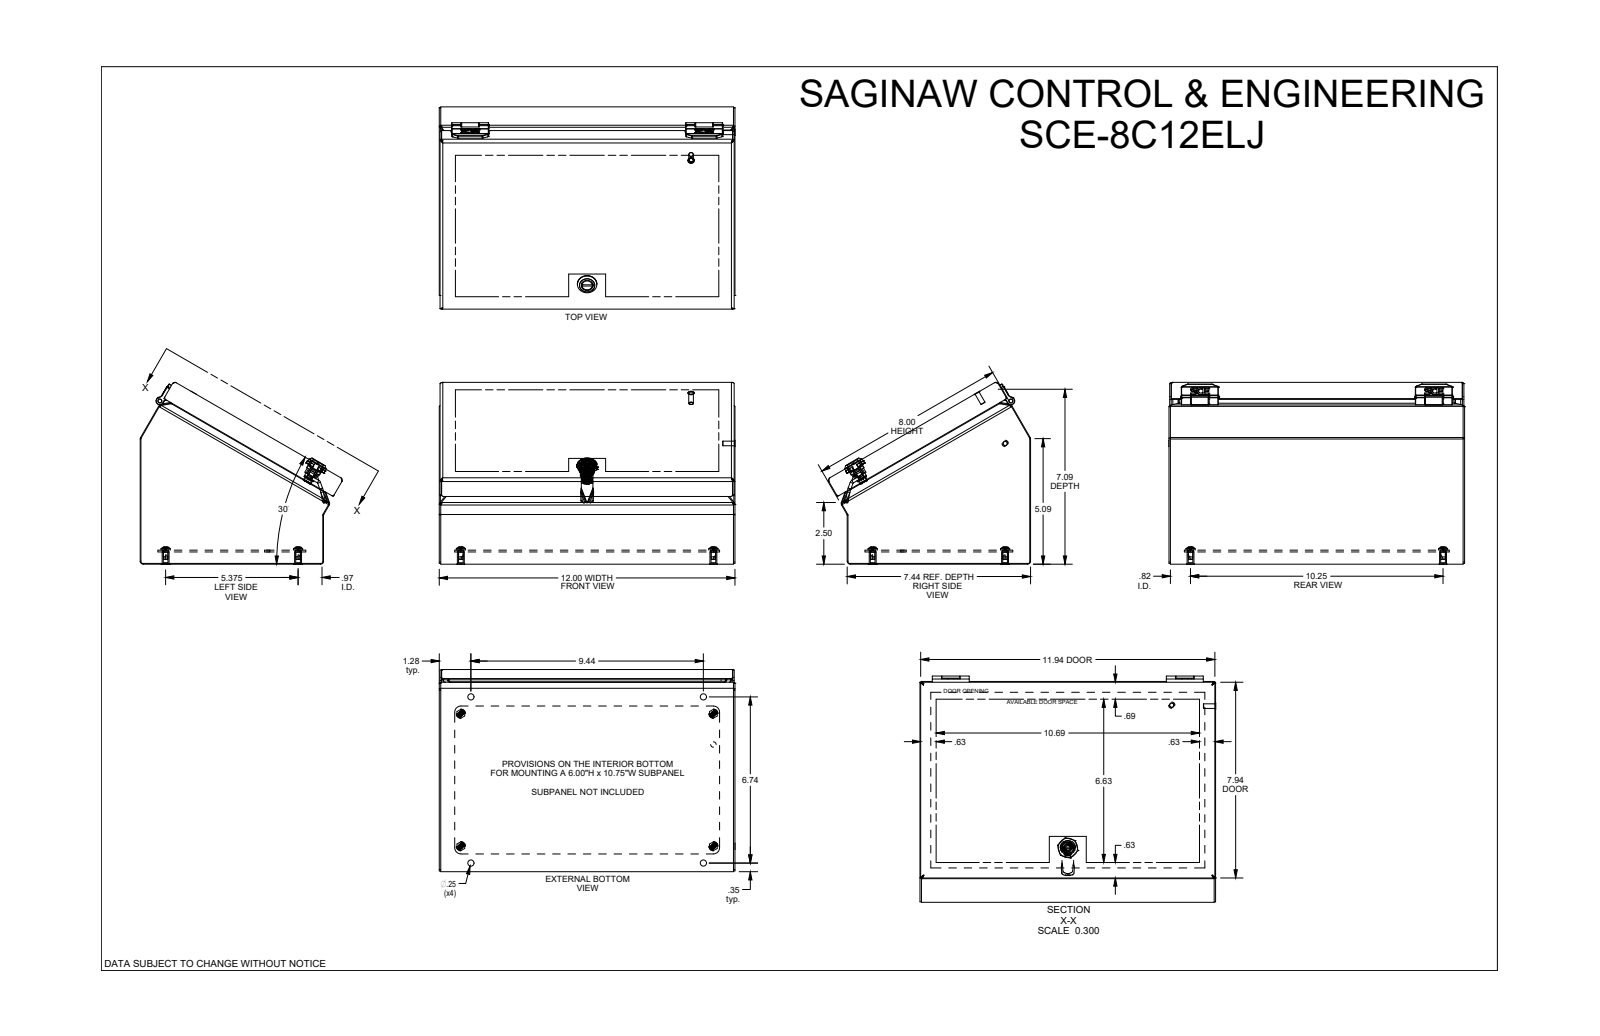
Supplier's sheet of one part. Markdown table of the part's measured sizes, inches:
| quantity | value |
| --- | --- |
| part name | SCE-8C12ELJ |
| STEP written by | SolidWorks 2019 (AUTOMOTIVE_DESIGN) |
| units | inches |
| bodies | 24 solids, 1046 faces (426 planar, 434 cylindrical, 186 other) |
| overall size | 12.004 × 8.201 × 7.38 |
| volume | 33.8 in³ |
| surface area | 1 059 in² |
| round holes (diameter × count) | 0.25 × 8, 0.19 × 4, 0.281 × 4, 0.02 × 2, 0.1 × 2, 0.174 × 2, 0.193 × 2, 0.266 × 2, 0.158 × 1, 0.188 × 1, 0.2 × 1, 0.218 × 1 |
| round bosses / shafts (diameter × count) | 0.28 × 4, 0.26 × 2, 0.256 × 2, 0.188 × 2, 0.18 × 2, 0.788 × 1, 0.548 × 1, 0.46 × 1 |
| partial cylindrical surfaces (radius × count) | 0.008 × 32, 0.03 × 24, 0.06 × 22, 0.013 × 21, 0.015 × 20, 0.12 × 16, 0.01 × 14, 0.02 × 9 |
| main face-to-face distances | 0.06, 0.06, 11.94, 0.436, 0.496, 0.075, 0.511, 0.571, 7.382, 11.88 |
| hole center spacings | 0.795, 6.072, 9.868, 11.559, 5.375, 6.742, 9.438, 9.5 |
